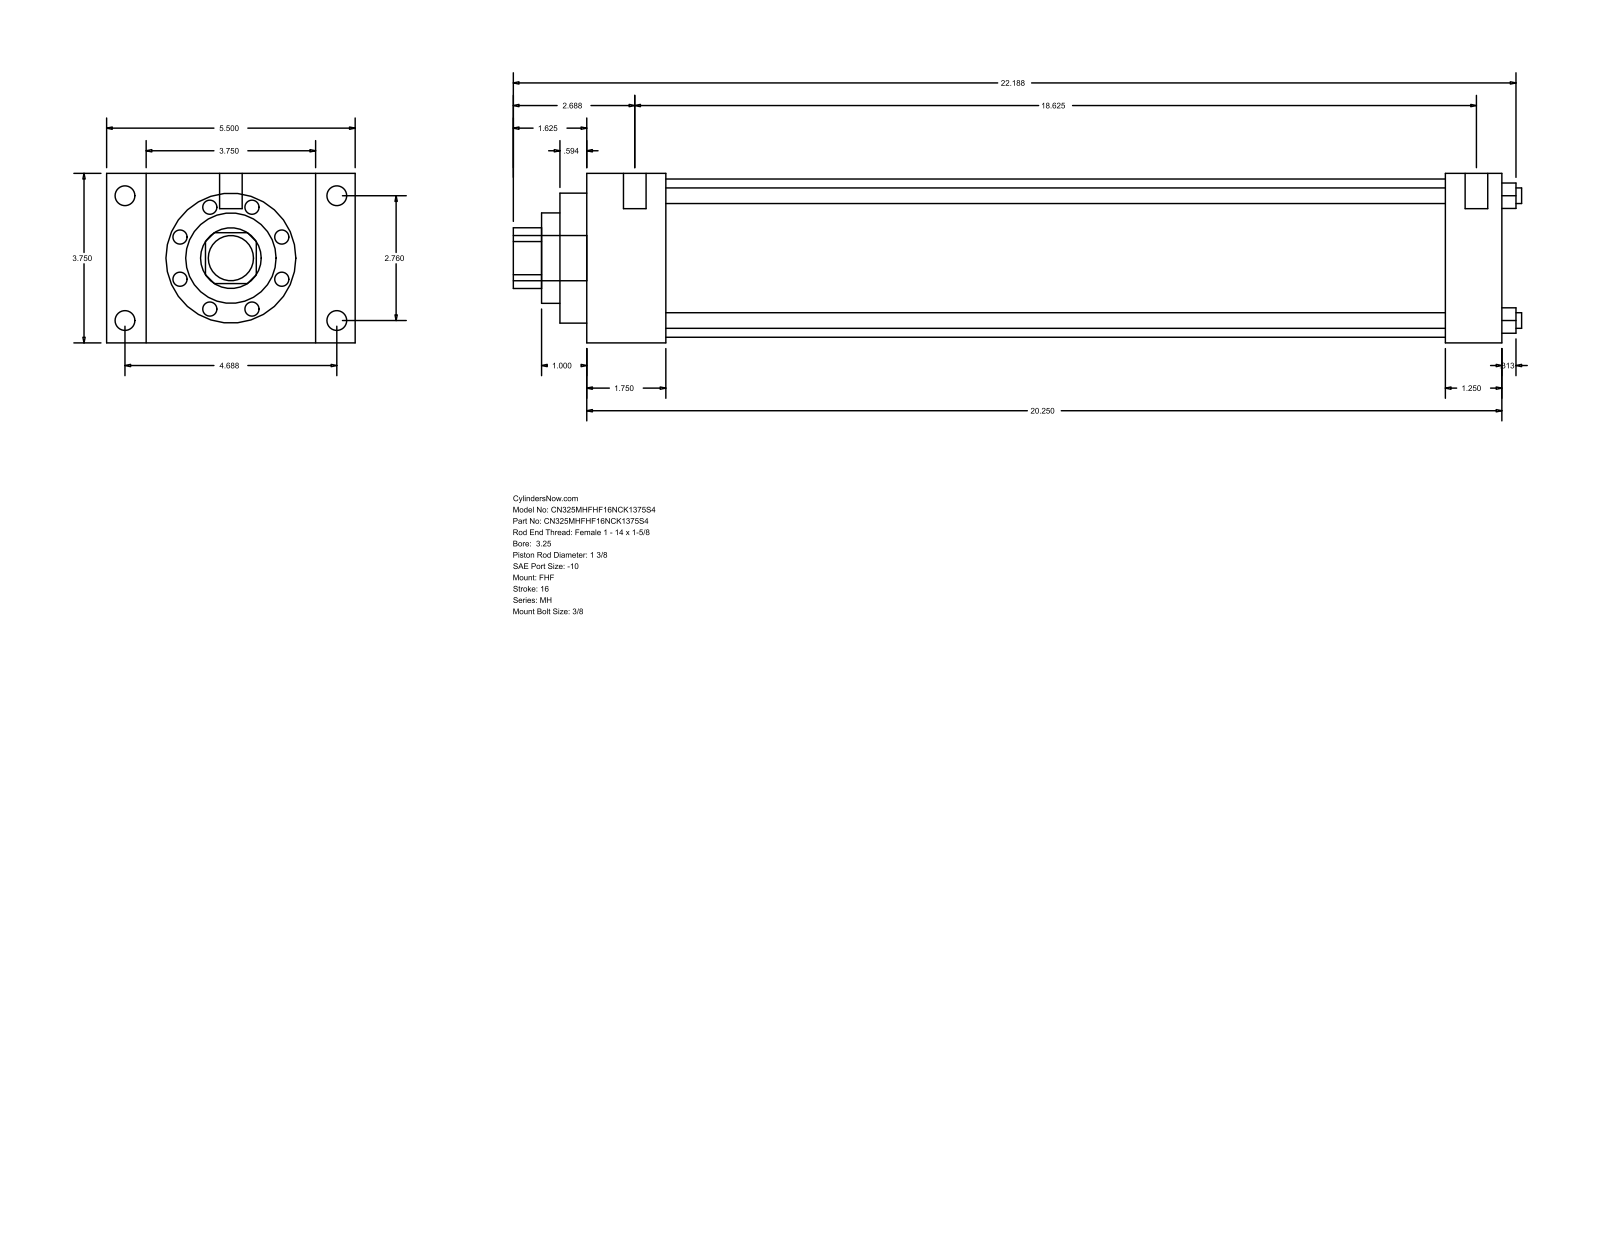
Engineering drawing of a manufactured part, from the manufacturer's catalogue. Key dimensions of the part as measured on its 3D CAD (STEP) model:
Part name (STEP PRODUCT): MH_FHF__0325_1.375
STEP written by: GSSL Pune (CONFIG_CONTROL_DESIGN)
Units: millimetres
Bodies: 0 solids, 90 faces (61 planar, 29 cylindrical, 0 other)
Overall size (bounding box): 566.74 × 139.7 × 95.25
Round holes (diameter × count): ⌀8.76 ×4, ⌀34.92 ×1, ⌀50.8 ×1, ⌀73.03 ×1, ⌀88.9 ×1
Round bosses / shafts (diameter × count): ⌀11.13 ×4, ⌀5.56 ×4, ⌀12.7 ×2, ⌀25.4 ×1
Partial cylindrical surfaces — rounded edges, fillets, slot ends (radius × count): R17.06 ×1
Main face-to-face distances: 95.24, 514.35, 44.45, 469.9, 22.23, 117.47, 139.7, 482.61, 438.16, 31.74
Hole centre spacings: 49.57, 70.1, 99.14
